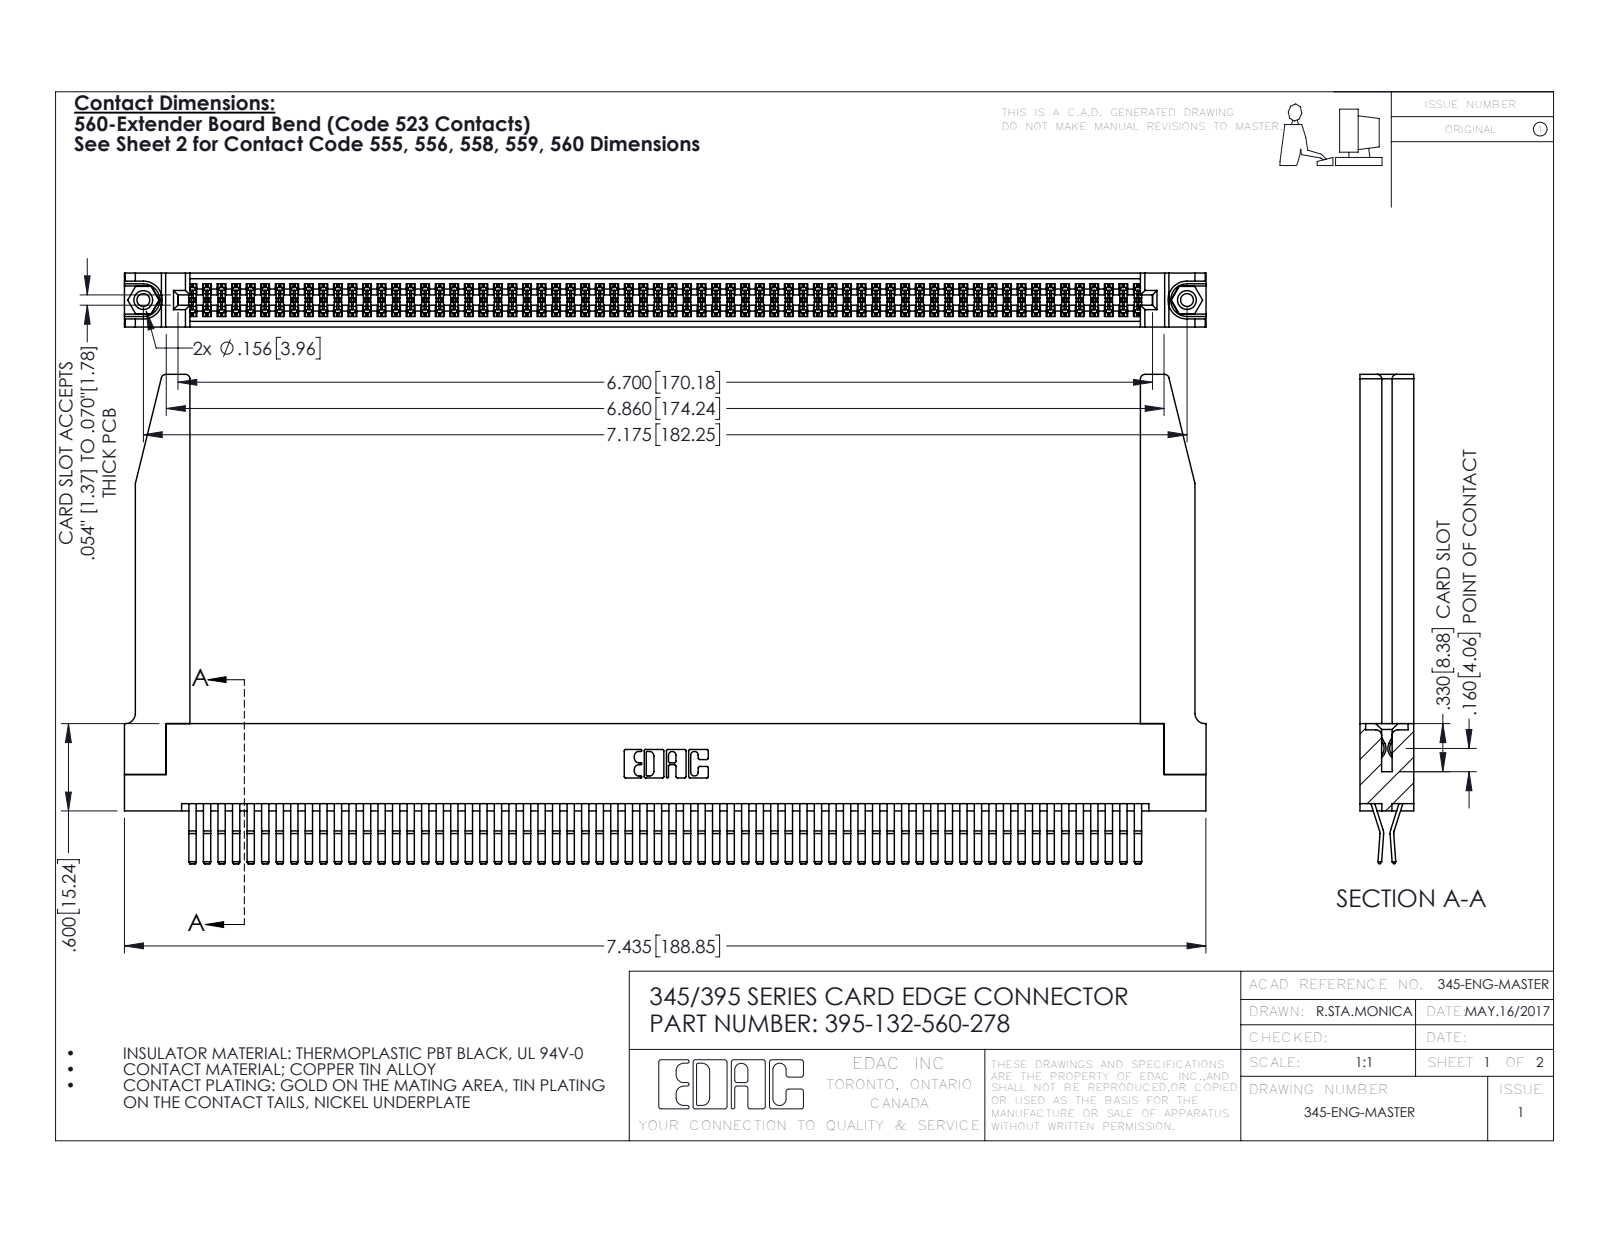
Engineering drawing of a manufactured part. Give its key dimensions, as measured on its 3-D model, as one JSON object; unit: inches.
{"part_name": "345 Part_Flush Mounting Lugs - 0.156 Dia-TH; 345-250-001_345-250-001-102; 345-220-078_345-220-078; 395-132-560-278 (+1 more)", "step_written_by": "SolidWorks 2016 (CONFIG_CONTROL_DESIGN)", "units": "inches", "bodies": {"solids": 137, "faces": 7224, "planar": 4578, "cylindrical": 2594, "other": 52}, "overall_size": [7.436, 3.362, 0.37], "volume_in3": 1.66, "surface_area_in2": 59.3, "round_holes": [[0.089, 2], [0.125, 2], [0.156, 2], [0.064, 1]], "round_bosses_or_shafts": [[0.155, 2]], "partial_cylinders_radius": [[0.006, 199], [0.01, 22], [0.03, 8], [0.007, 6], [0.031, 6], [0.026, 3], [0.01, 2], [0.014, 2]], "face_to_face_distances": [0.072, 0.298, 0.025, 0.37, 0.2, 0.098, 0.272, 0.225, 0.175, 0.149], "hole_center_spacings": [0.27, 6.939, 7.175]}
